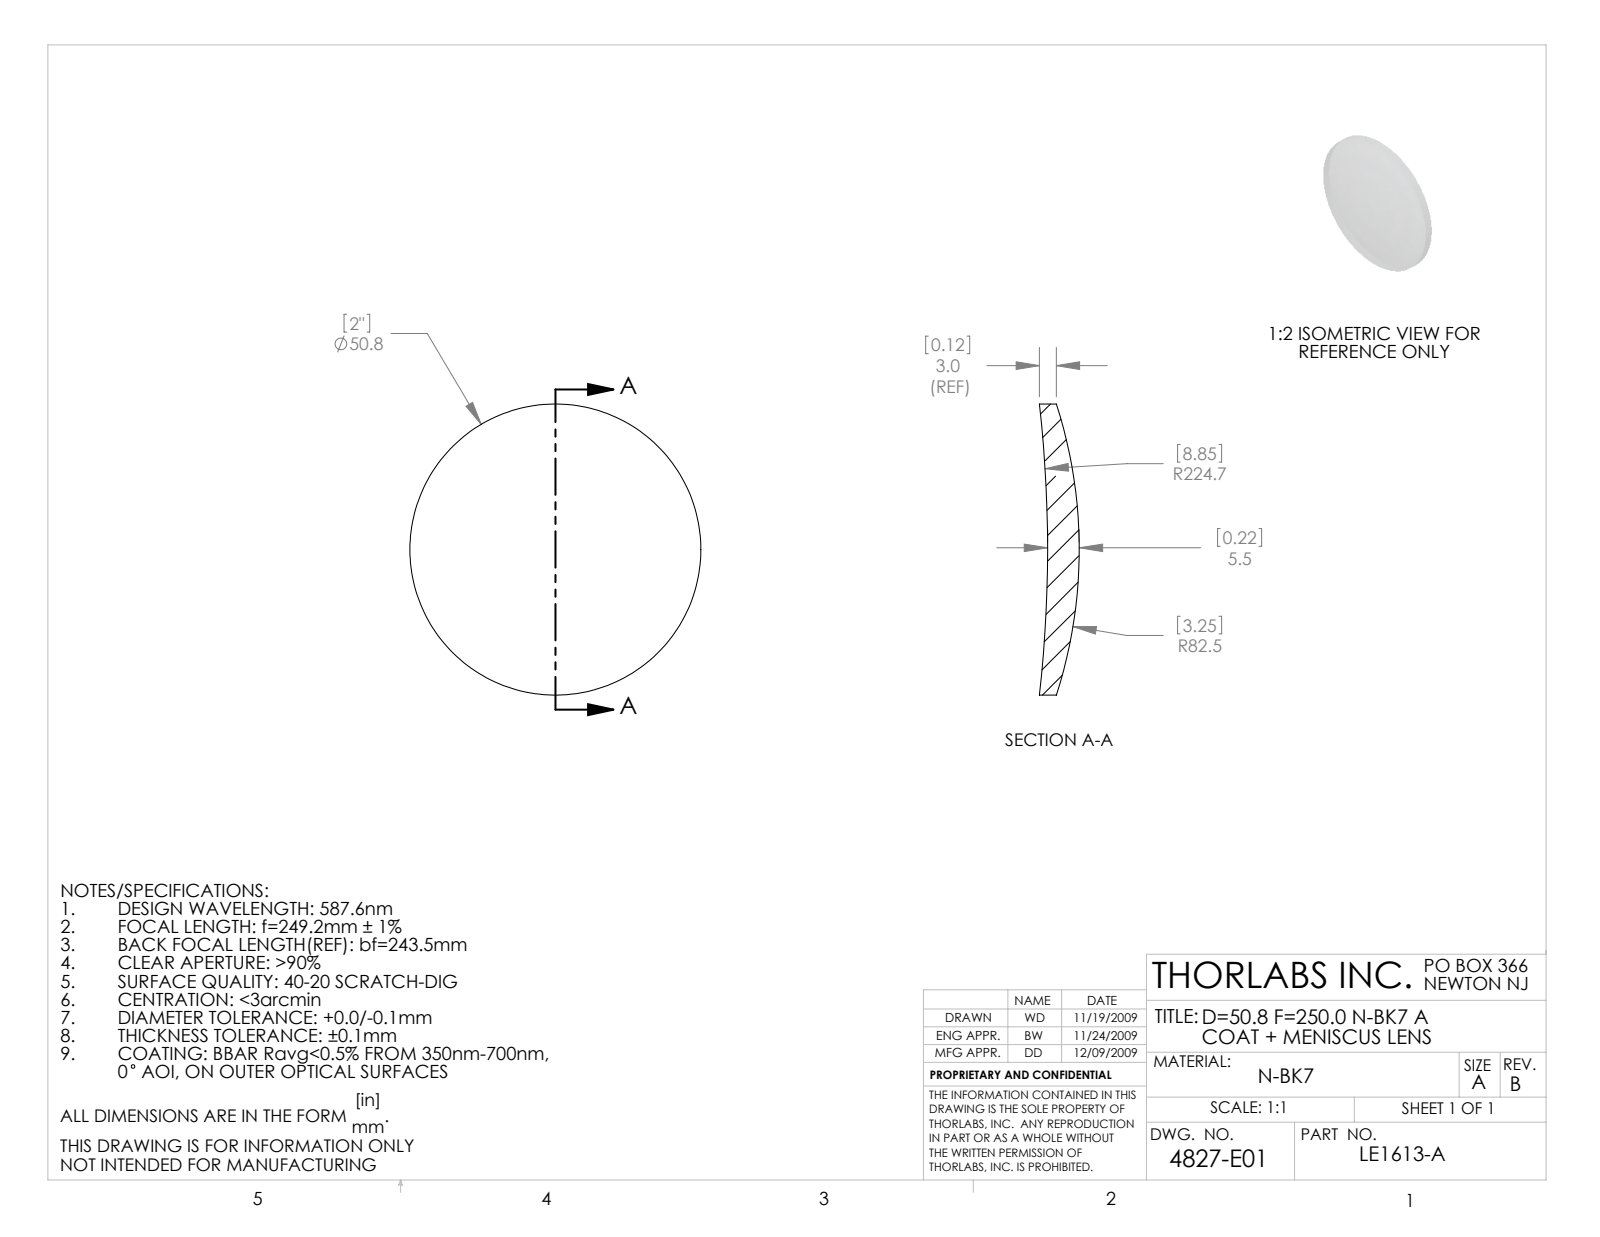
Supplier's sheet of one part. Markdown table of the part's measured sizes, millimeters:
| quantity | value |
| --- | --- |
| part name | 4827-E0W |
| STEP written by | SolidWorks 2009 (AUTOMOTIVE_DESIGN) |
| units | millimeters |
| bodies | 1 solid, 6 faces (0 planar, 2 cylindrical, 4 other) |
| overall size | 50.8 × 50.8 × 6.97 |
| volume | 8 641 mm³ |
| surface area | 4 584 mm² |
| round bosses / shafts (diameter × count) | 50.8 × 1 |
